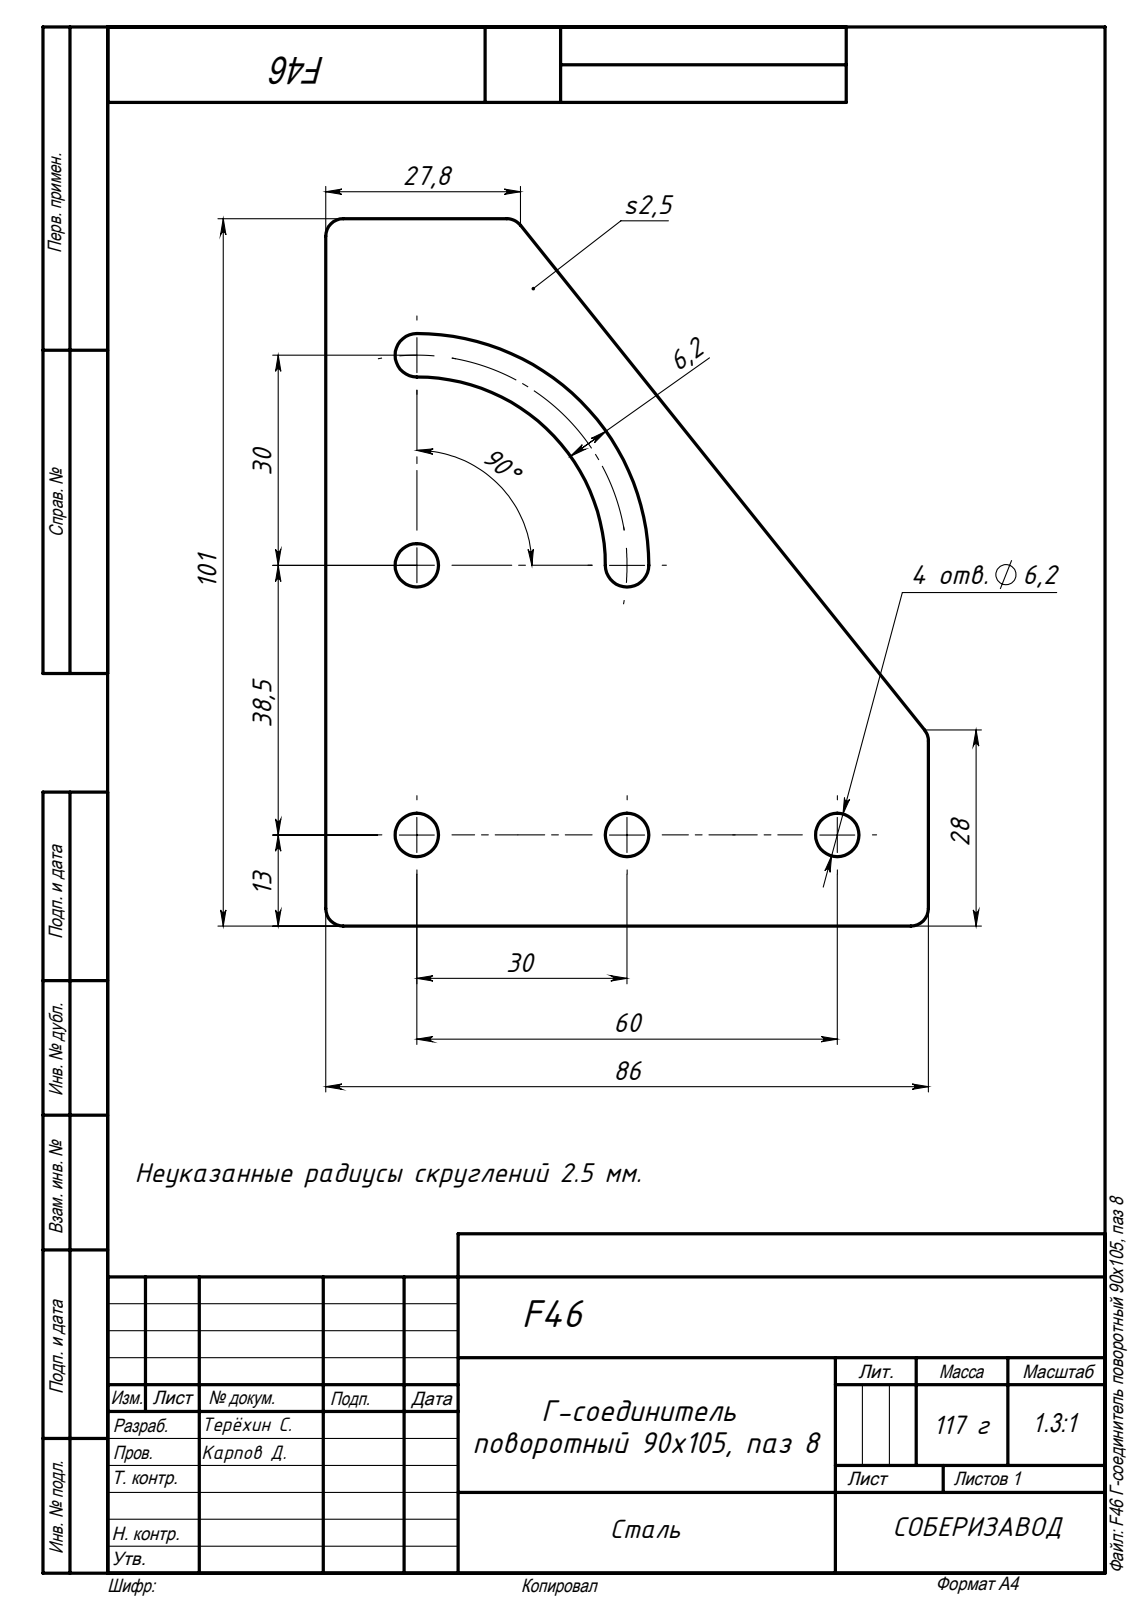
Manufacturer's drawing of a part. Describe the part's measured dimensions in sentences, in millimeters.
The part is named "F46 Г-соединитель поворотный 90х105, паз 8". Its 3-D file was written by "SolidWorks 2020 (AUTOMOTIVE_DESIGN)". It is 1 solid with 24 faces: 7 planar, 17 cylindrical and 0 other. Overall it measures 101 by 86 by 2.5 millimeters. Its volume is 15 164 cubic millimeters and its surface area 13 441 square millimeters. Round holes: 4 of diameter 6.2. Partial cylindrical surfaces (rounded edges, fillets, slot ends): 5 of radius 2.5, 2 of radius 3.1, 1 of radius 26.9, 1 of radius 33.1. The main face-to-face distances are 2.5, 86, 101. The hole center spacings are 30, 38.5, 48.81, 60, 71.29.
